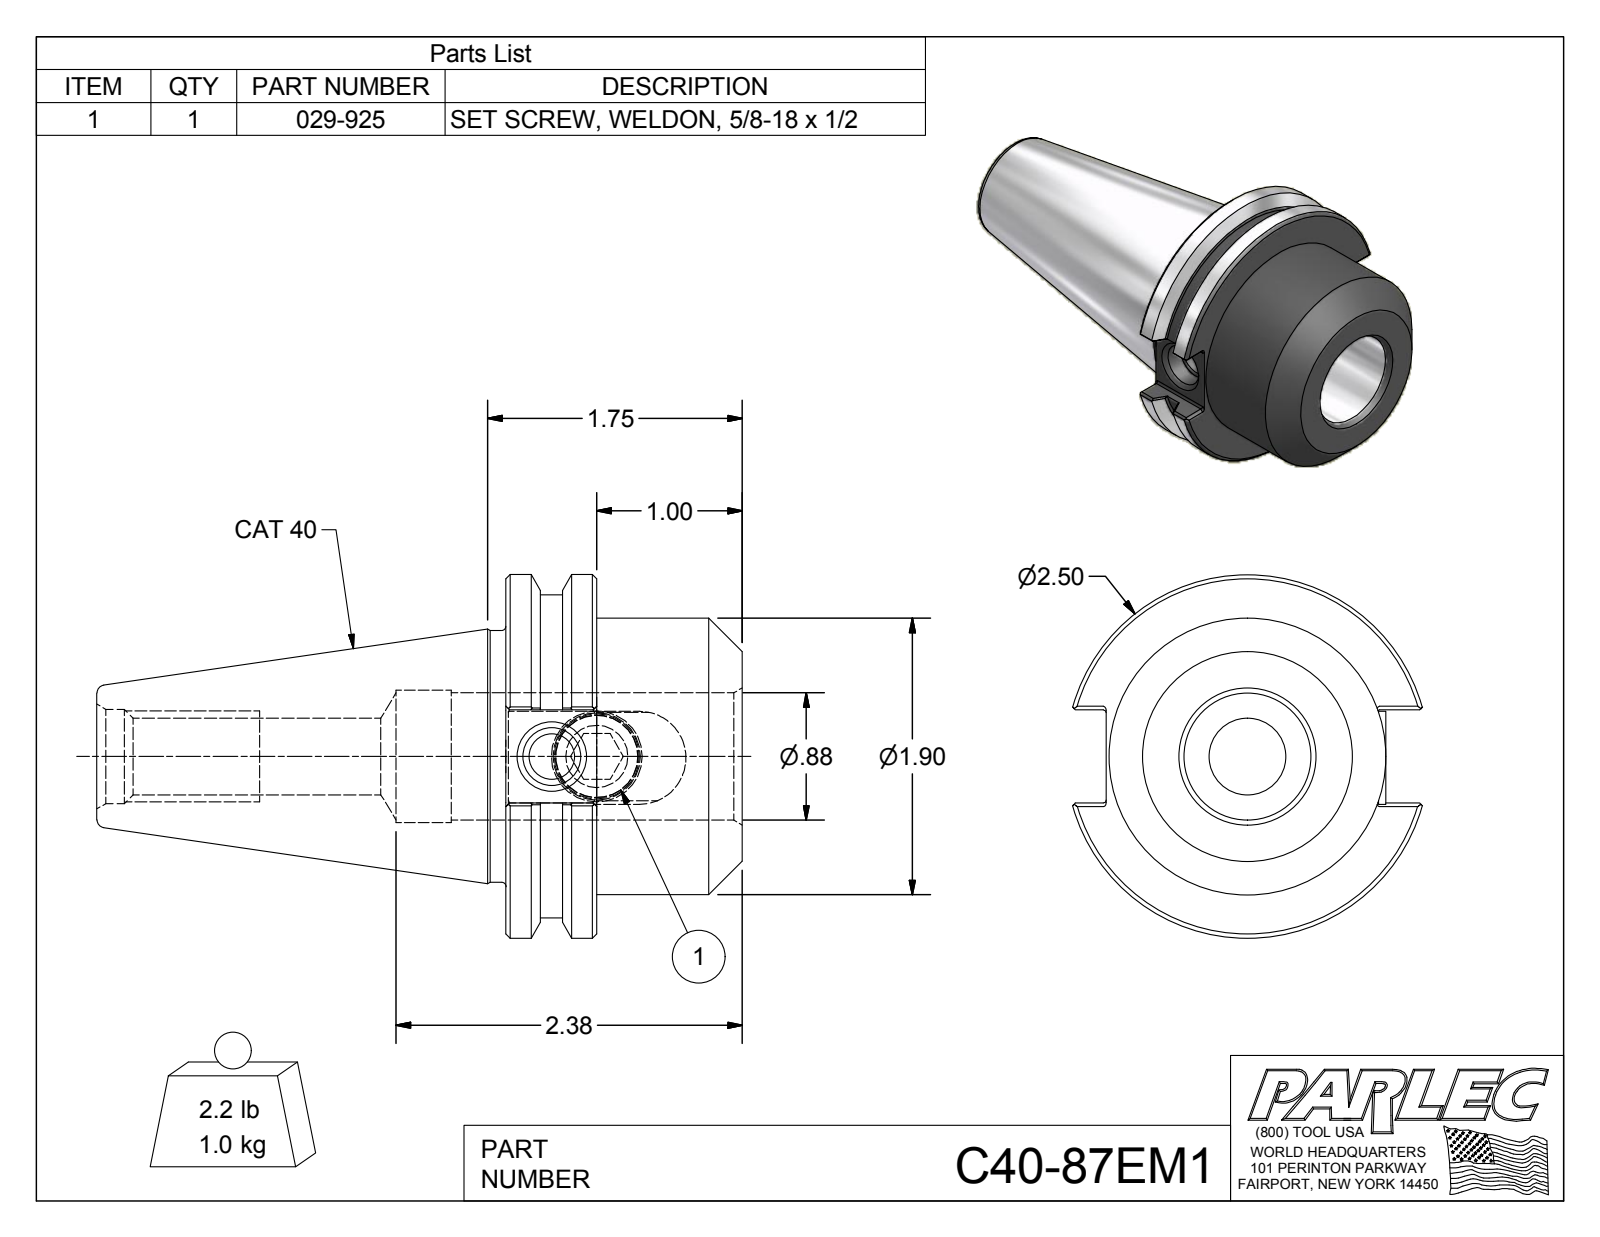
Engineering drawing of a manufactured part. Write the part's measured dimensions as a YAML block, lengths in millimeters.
part_name: "C40-87EM1; C40-87EM1-1; 029-925"
step_written_by: "Autodesk Inventor 2012 (AUTOMOTIVE_DESIGN)"
units: millimeters
bodies: {solids: 2, faces: 110, planar: 49, cylindrical: 30, other: 31}
overall_size: [112.7, 63.5, 61.1]
volume: 125900
surface_area: 28200
round_holes:
  - {diameter: 8, count: 1}
  - {diameter: 10.1, count: 1}
  - {diameter: 13.4, count: 1}
  - {diameter: 14.4, count: 1}
  - {diameter: 16.5, count: 1}
  - {diameter: 22.2, count: 1}
  - {diameter: 23.1, count: 1}
round_bosses_or_shafts:
  - {diameter: 63.5, count: 1}
  - {diameter: 56.4, count: 1}
  - {diameter: 48.3, count: 1}
  - {diameter: 43.9, count: 1}
  - {diameter: 15.9, count: 1}
partial_cylinders:
  - {radius: 0.5, count: 12}
  - {radius: 8.1, count: 1}
face_to_face_distances: [15.9, 25.4, 41.3, 1.3, 1.6, 8, 48.8, 47.5, 47.2, 16.3]
hole_center_spacings: [7.9]
